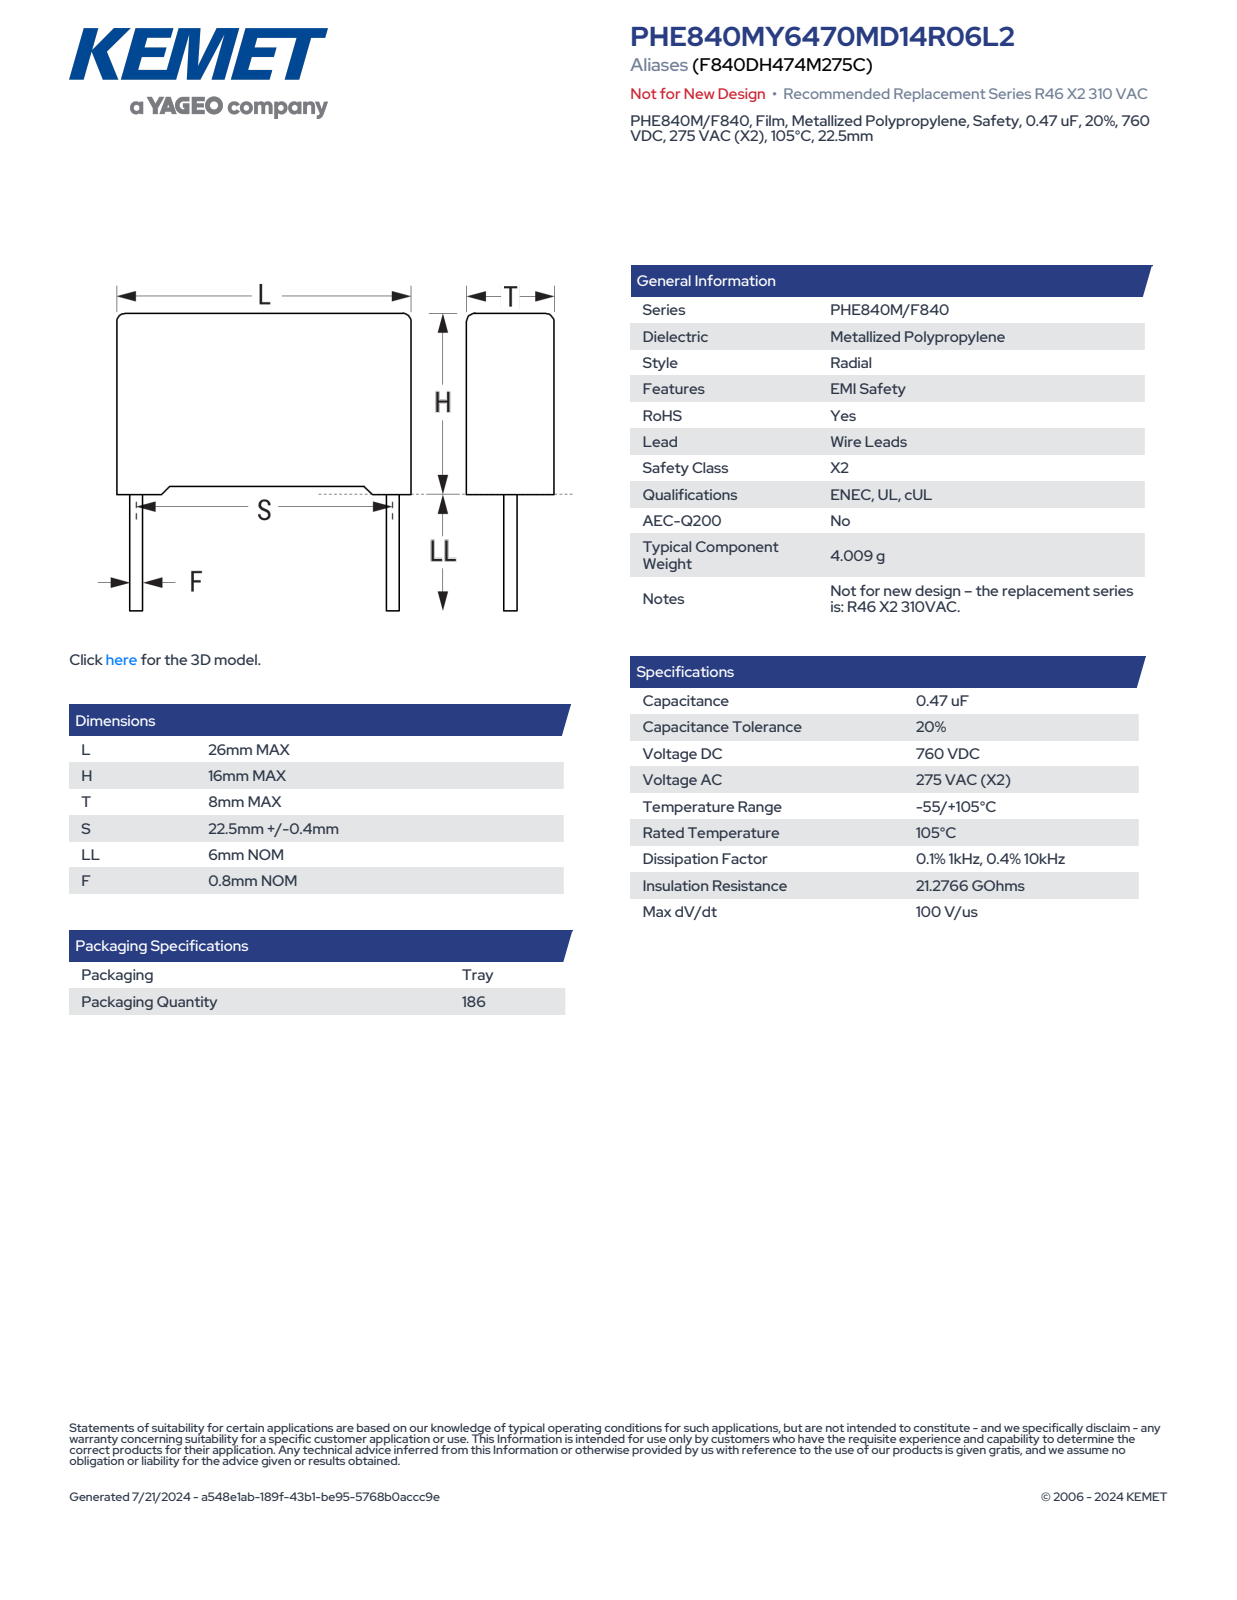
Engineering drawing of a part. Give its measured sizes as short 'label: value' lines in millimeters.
name: CFR_RB2_26X16X8_L26H16T8S22.5LL6F0.8
written by: SolidWorks 2021 (AUTOMOTIVE_DESIGN)
unit: mm
bodies: 4 solids, 85 faces (77 planar, 8 cylindrical, 0 other)
size: 26 × 22 × 8.01
volume: 3 199 mm³; area: 1 579 mm²
bosses: 2× ⌀0.8
rounds: 4× R0.5
face distances: 8, 15.25, 26, 15.45, 0.87, 0.55, 0.75, 16, 7.13, 8.01
